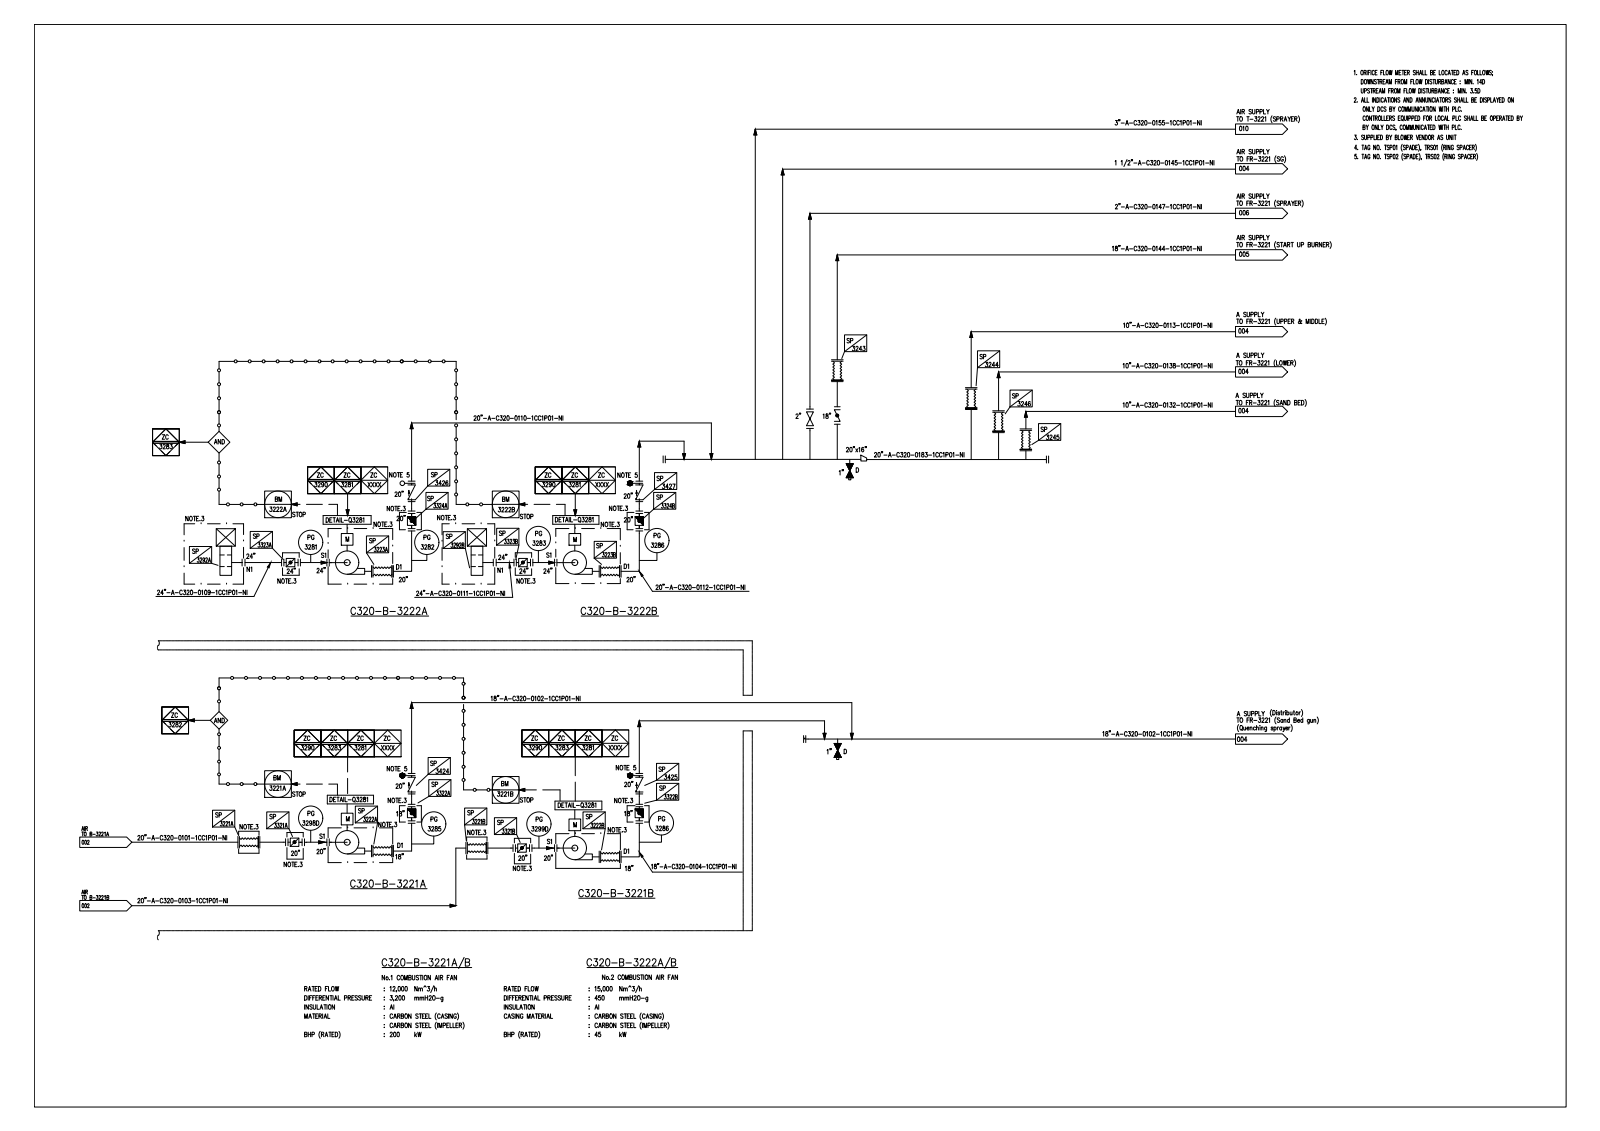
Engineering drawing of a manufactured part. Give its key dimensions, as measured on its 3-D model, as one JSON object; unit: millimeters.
{"part_name": "Sample", "step_written_by": "Autodesk Inventor 2020 (AUTOMOTIVE_DESIGN)", "units": "millimeters", "bodies": {"solids": 1, "faces": 11, "planar": 2, "cylindrical": 0, "other": 9}, "overall_size": [112.43, 101.42, 56.64], "volume_mm3": 24408, "surface_area_mm2": 27845, "face_to_face_distances": [1.9]}
